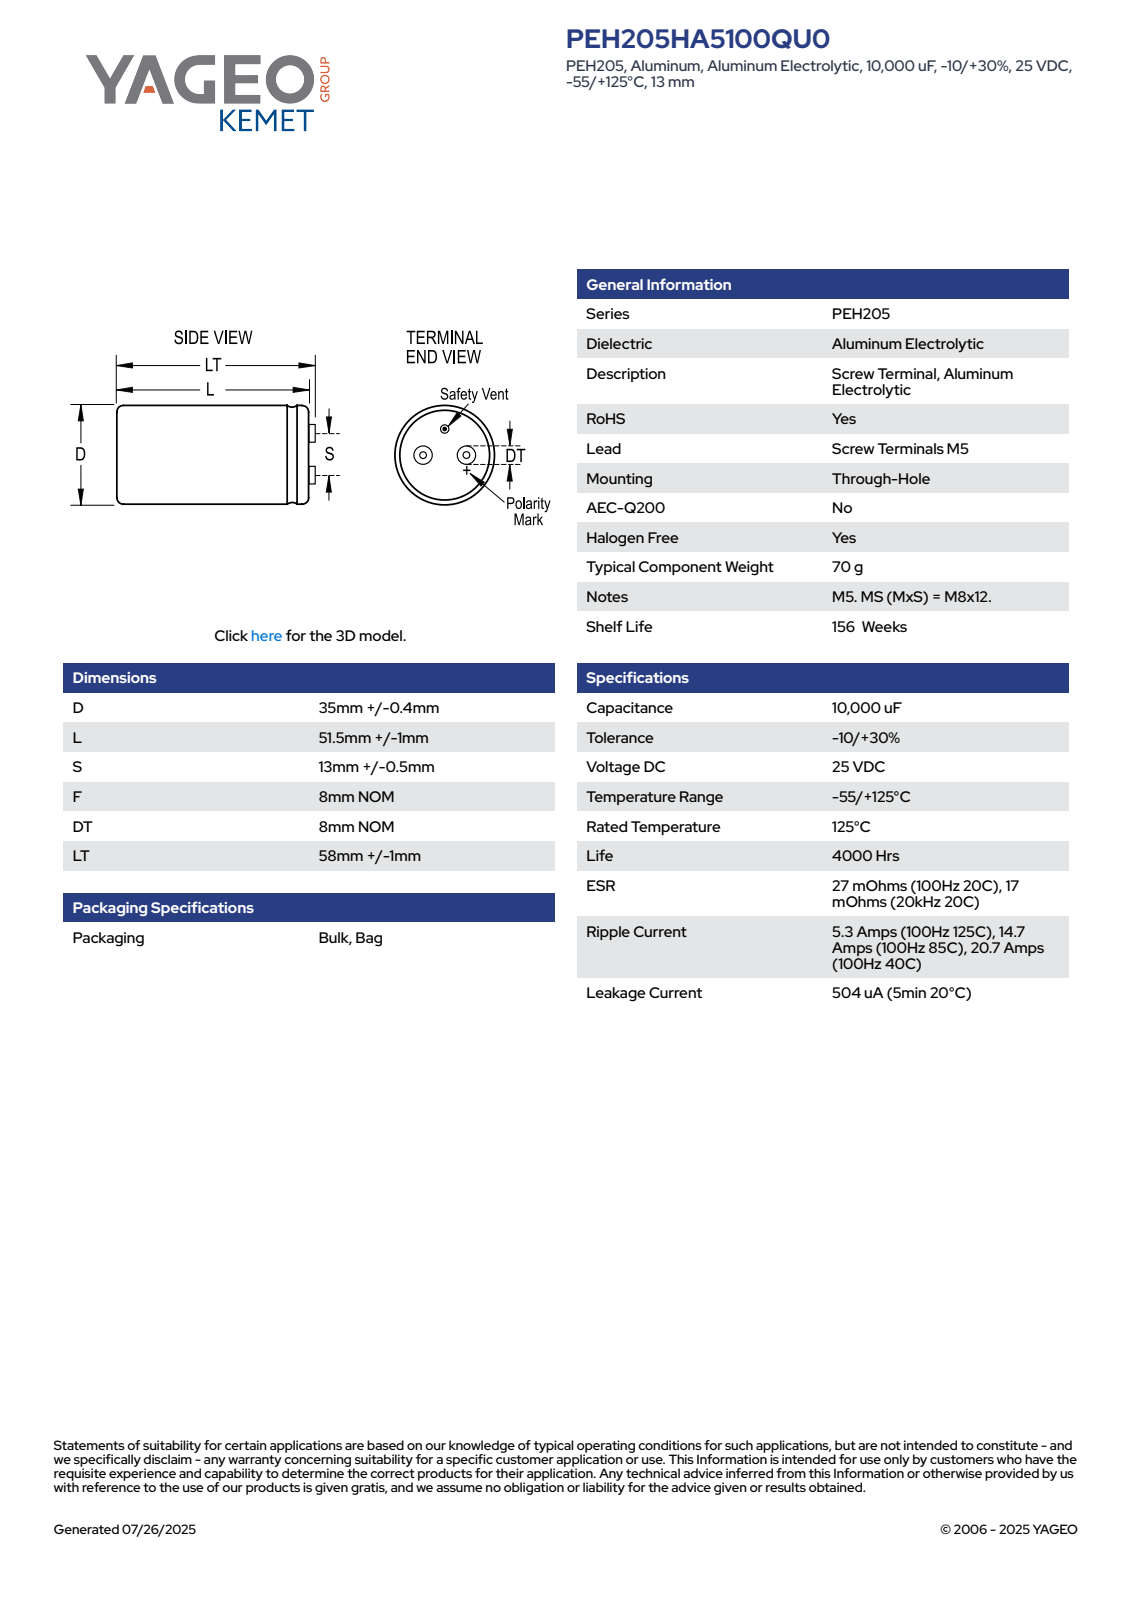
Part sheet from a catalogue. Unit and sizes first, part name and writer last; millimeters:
Units: millimetres
Overall size (bounding box): 57 × 35.4 × 35.4
Round holes (diameter × count): ⌀2.5 ×2, ⌀2 ×1, ⌀31.4 ×1
Round bosses / shafts (diameter × count): ⌀8 ×2, ⌀35.4 ×1, ⌀3 ×1
Partial cylindrical surfaces — rounded edges, fillets, slot ends (radius × count): R17.69 ×1
Main face-to-face distances: 51.5, 57, 5.5, 52, 0.5, 5, 44.18, 7.32, 7.82, 12.82
Hole centre spacings: 6.5, 11.1, 9, 13
Volume: 50 544 mm³ · Surface area: 8 288 mm²
Bodies: 1 solid, 87 faces (30 planar, 21 cylindrical, 36 other)
Part name (STEP PRODUCT): CARC_D35.4L52.5S13
STEP written by: SolidWorks 2021 (AUTOMOTIVE_DESIGN)
